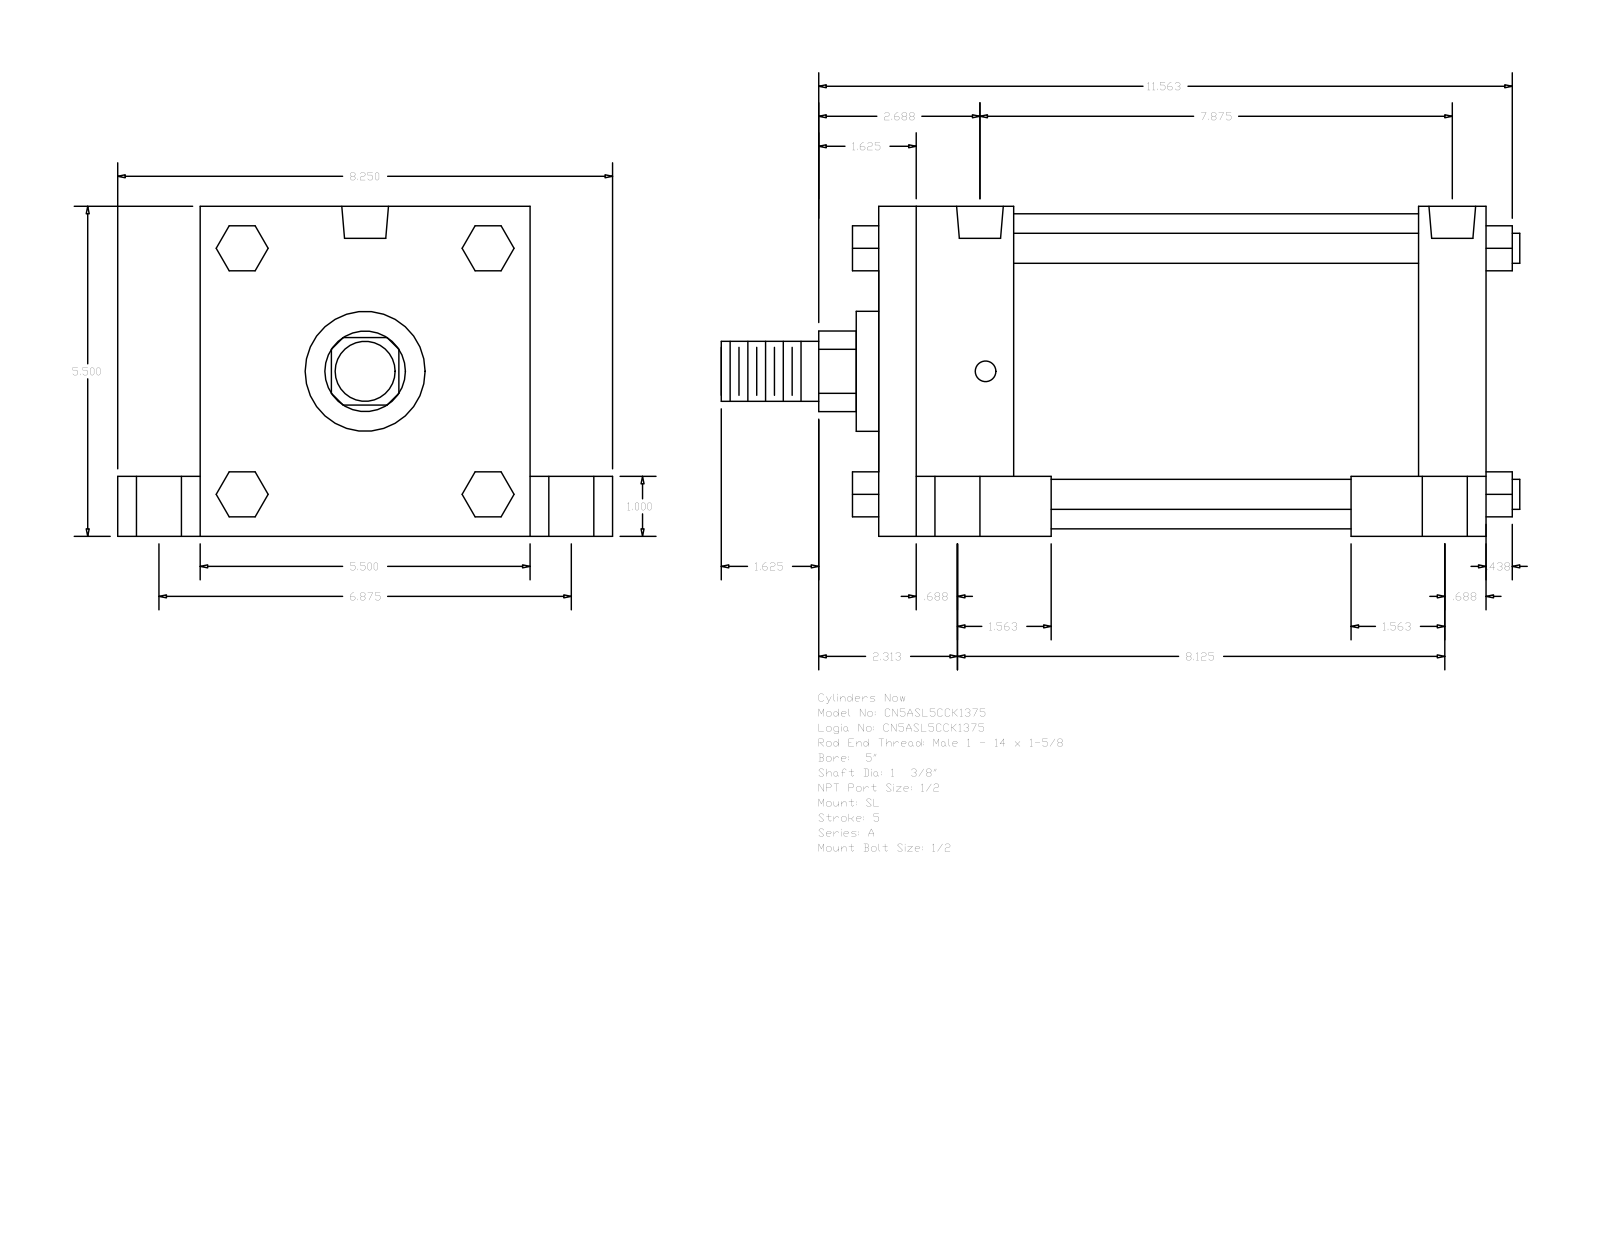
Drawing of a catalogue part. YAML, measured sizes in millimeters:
part_name: "A_SL__0500_1.375"
step_written_by: "GSSL Pune (CONFIG_CONTROL_DESIGN)"
units: millimeters
bodies: {solids: 0, faces: 150, planar: 114, cylindrical: 36, other: 0}
overall_size: [338.14, 209.55, 139.7]
round_holes:
  - {diameter: 8.73, count: 4}
  - {diameter: 19.05, count: 4}
  - {diameter: 25.4, count: 4}
  - {diameter: 19.77, count: 2}
round_bosses_or_shafts:
  - {diameter: 12.7, count: 4}
  - {diameter: 133.35, count: 1}
  - {diameter: 50.8, count: 1}
  - {diameter: 34.92, count: 1}
  - {diameter: 25.4, count: 1}
partial_cylinders:
  - {radius: 17.06, count: 1}
face_to_face_distances: [139.7, 257.17, 57.15, 28.57, 25.4, 114.3, 34.93, 174.63, 228.6, 171.45]
hole_center_spacings: [2.39, 87.31, 87.37, 87.83, 88.12, 174.62, 195.25, 197.64]
